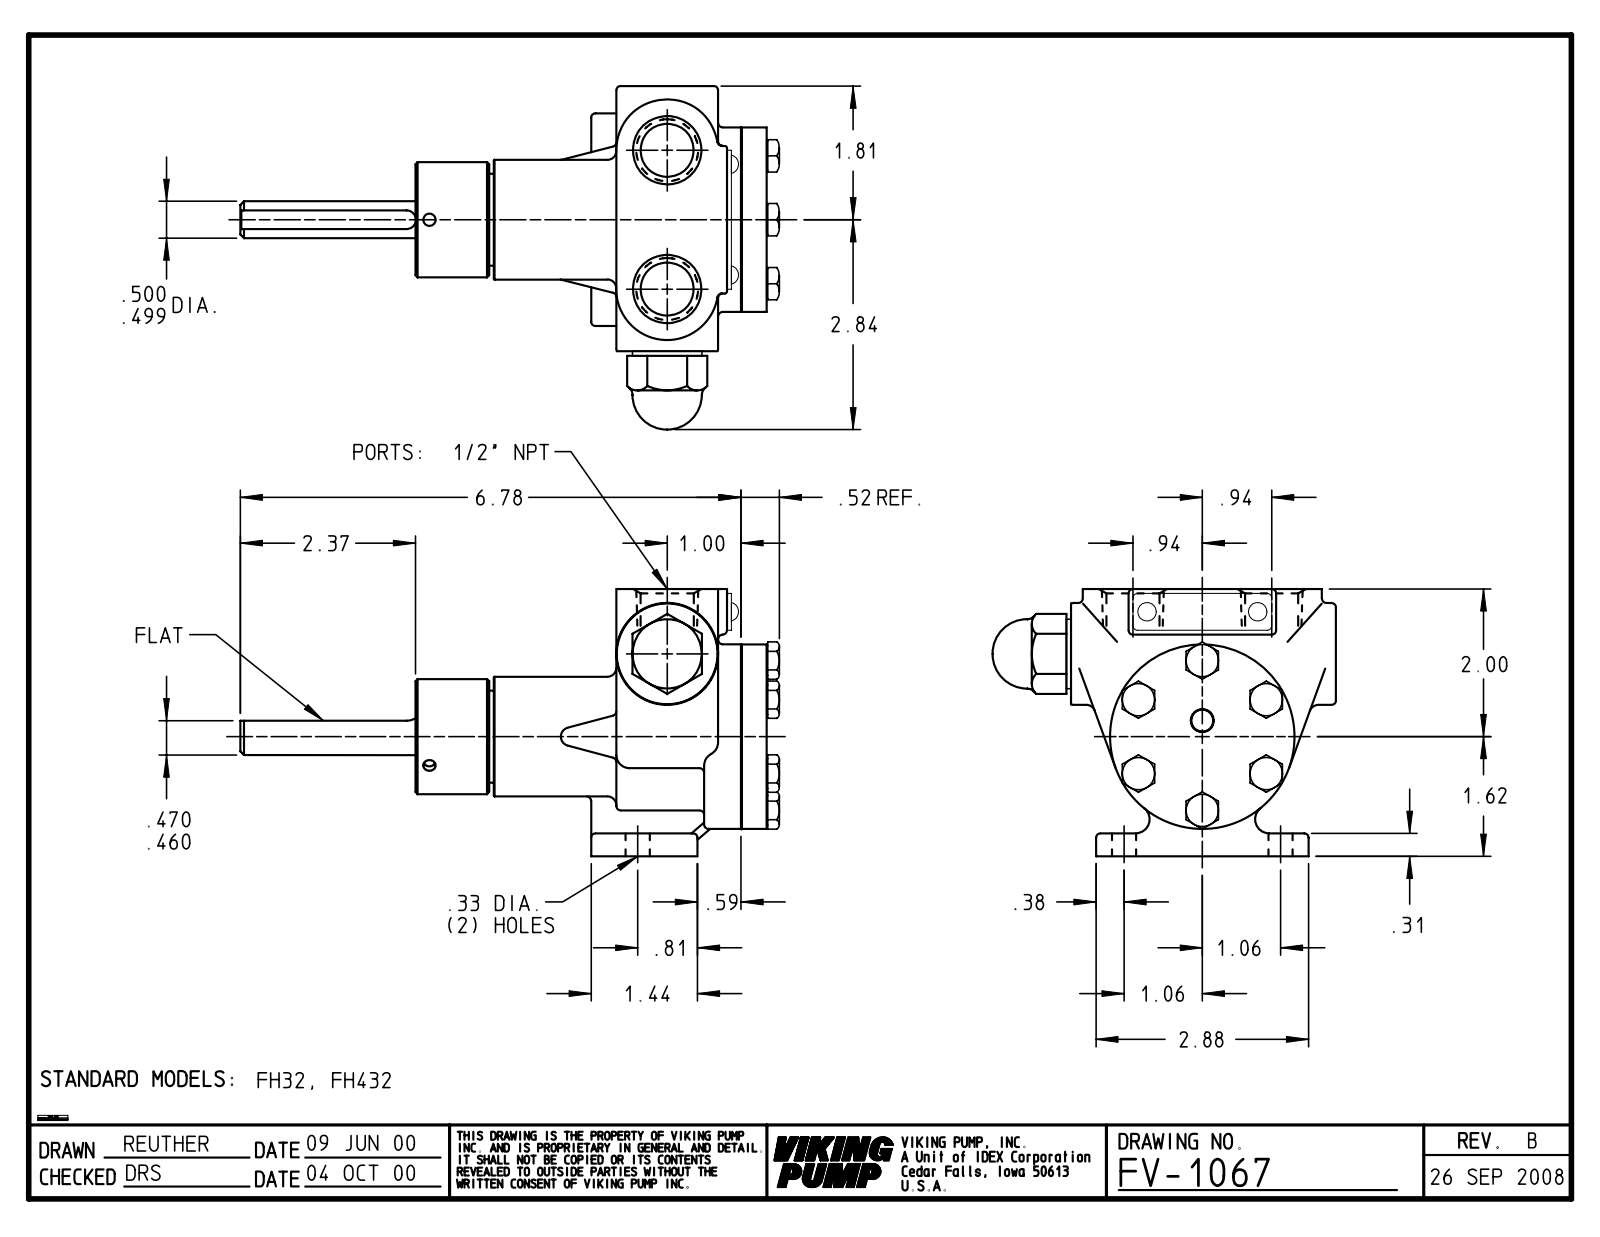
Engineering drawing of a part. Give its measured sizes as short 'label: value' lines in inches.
name: FV-1067
written by: SolidWorks 2024 (AUTOMOTIVE_DESIGN)
unit: in
bodies: 1 solid, 460 faces (135 planar, 41 cylindrical, 284 other)
size: 7.294 × 4.654 × 3.62
volume: 23.12 in³; area: 75.73 in²
holes: 2× ⌀0.129, 2× ⌀0.328, 1× ⌀0.311, 1× ⌀0.87, 1× ⌀1.015, 1× ⌀1.31
bosses: 6× ⌀0.438, 1× ⌀2.5, 1× ⌀2.498, 1× ⌀1.56, 1× ⌀1.246, 1× ⌀0.94, 1× ⌀0.5
rounds: 1× R0.156
face distances: 3.62, 4.777, 1.567, 1.567, 1.445, 1.445, 0.122, 0.357, 0.357, 1.802
hole spacings: 1.654, 1.849, 0.216, 1.5, 2.12
